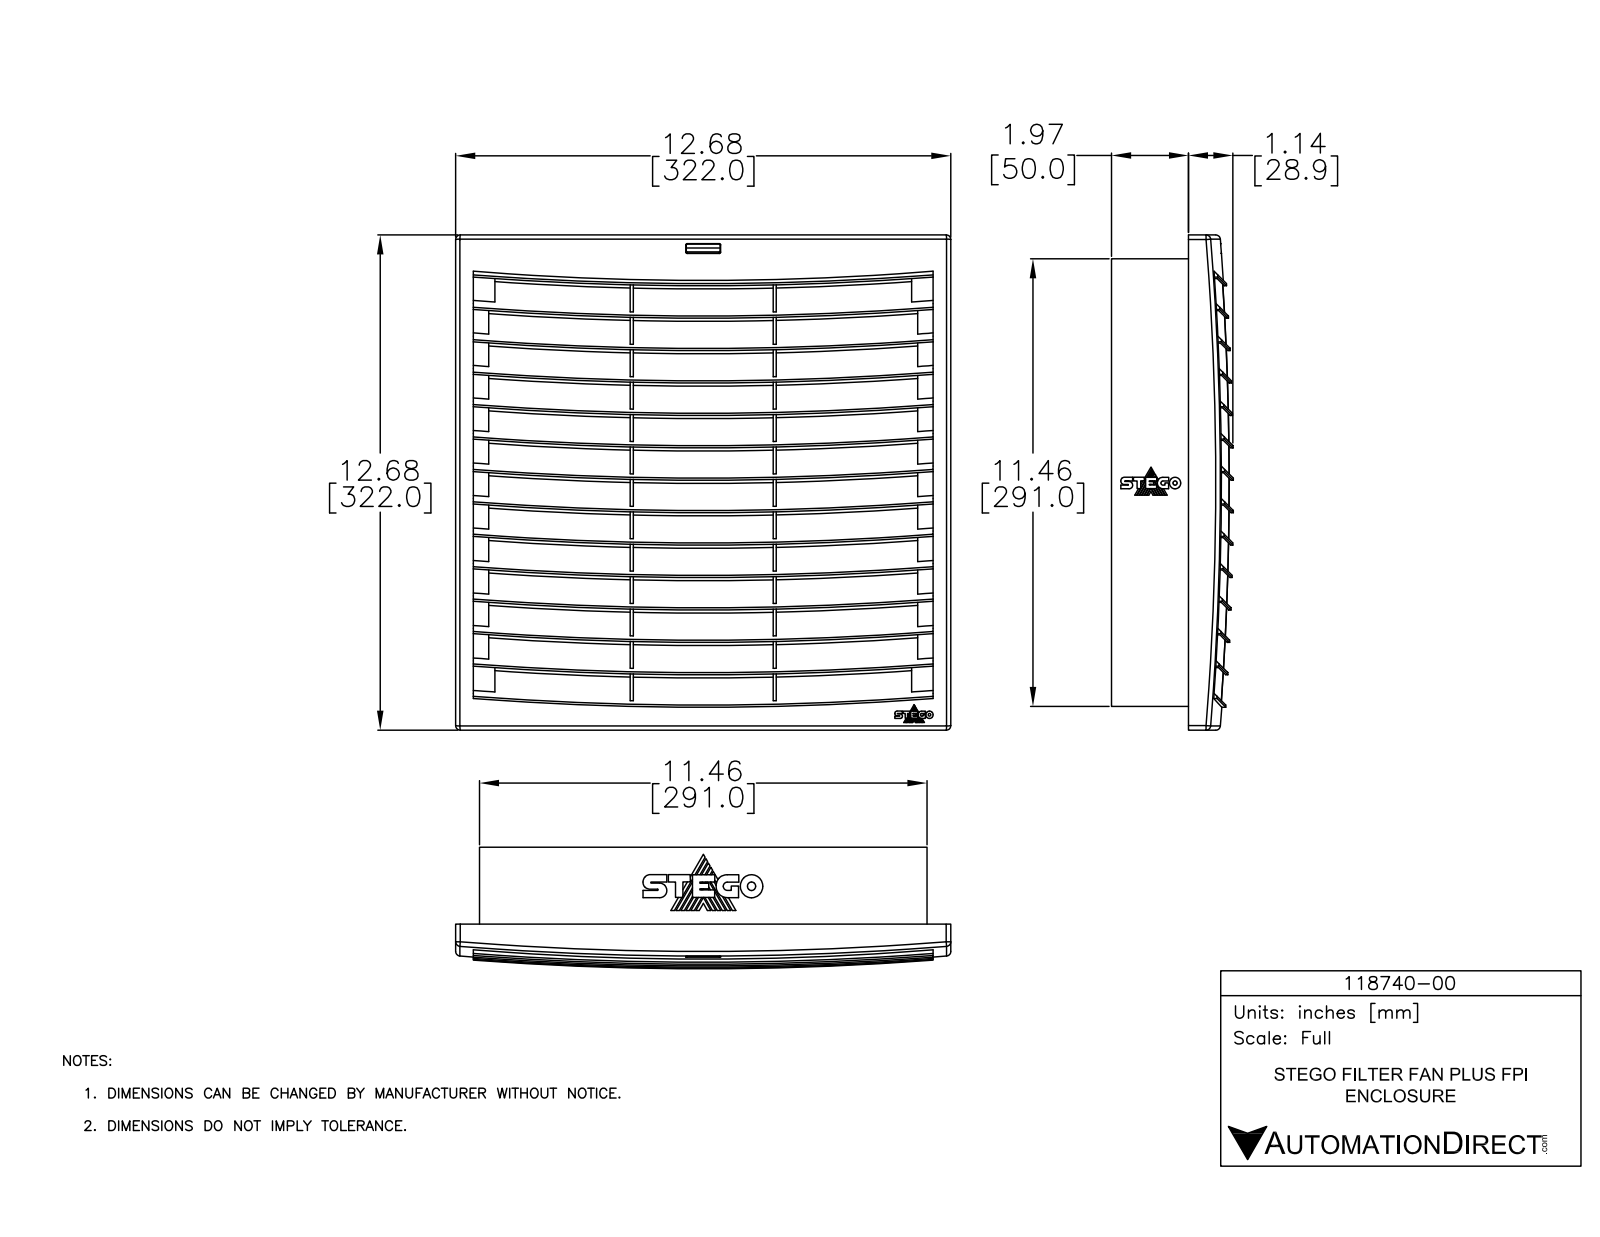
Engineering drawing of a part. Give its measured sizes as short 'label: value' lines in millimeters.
name: 11874_Test_4
written by: SolidWorks 2016 (AUTOMOTIVE_DESIGN)
unit: mm
bodies: 2 solids, 667 faces (351 planar, 53 cylindrical, 263 other)
size: 322 × 322 × 79.2
volume: 4 775 000 mm³; area: 616 959 mm²
rounds: 13× R1375.09, 4× R0.5, 4× R1, 4× R3, 1× R2.34, 1× R2.6
face distances: 2, 52, 291, 300.5, 19.5, 304.5, 15.5, 13.5, 50, 306.5
